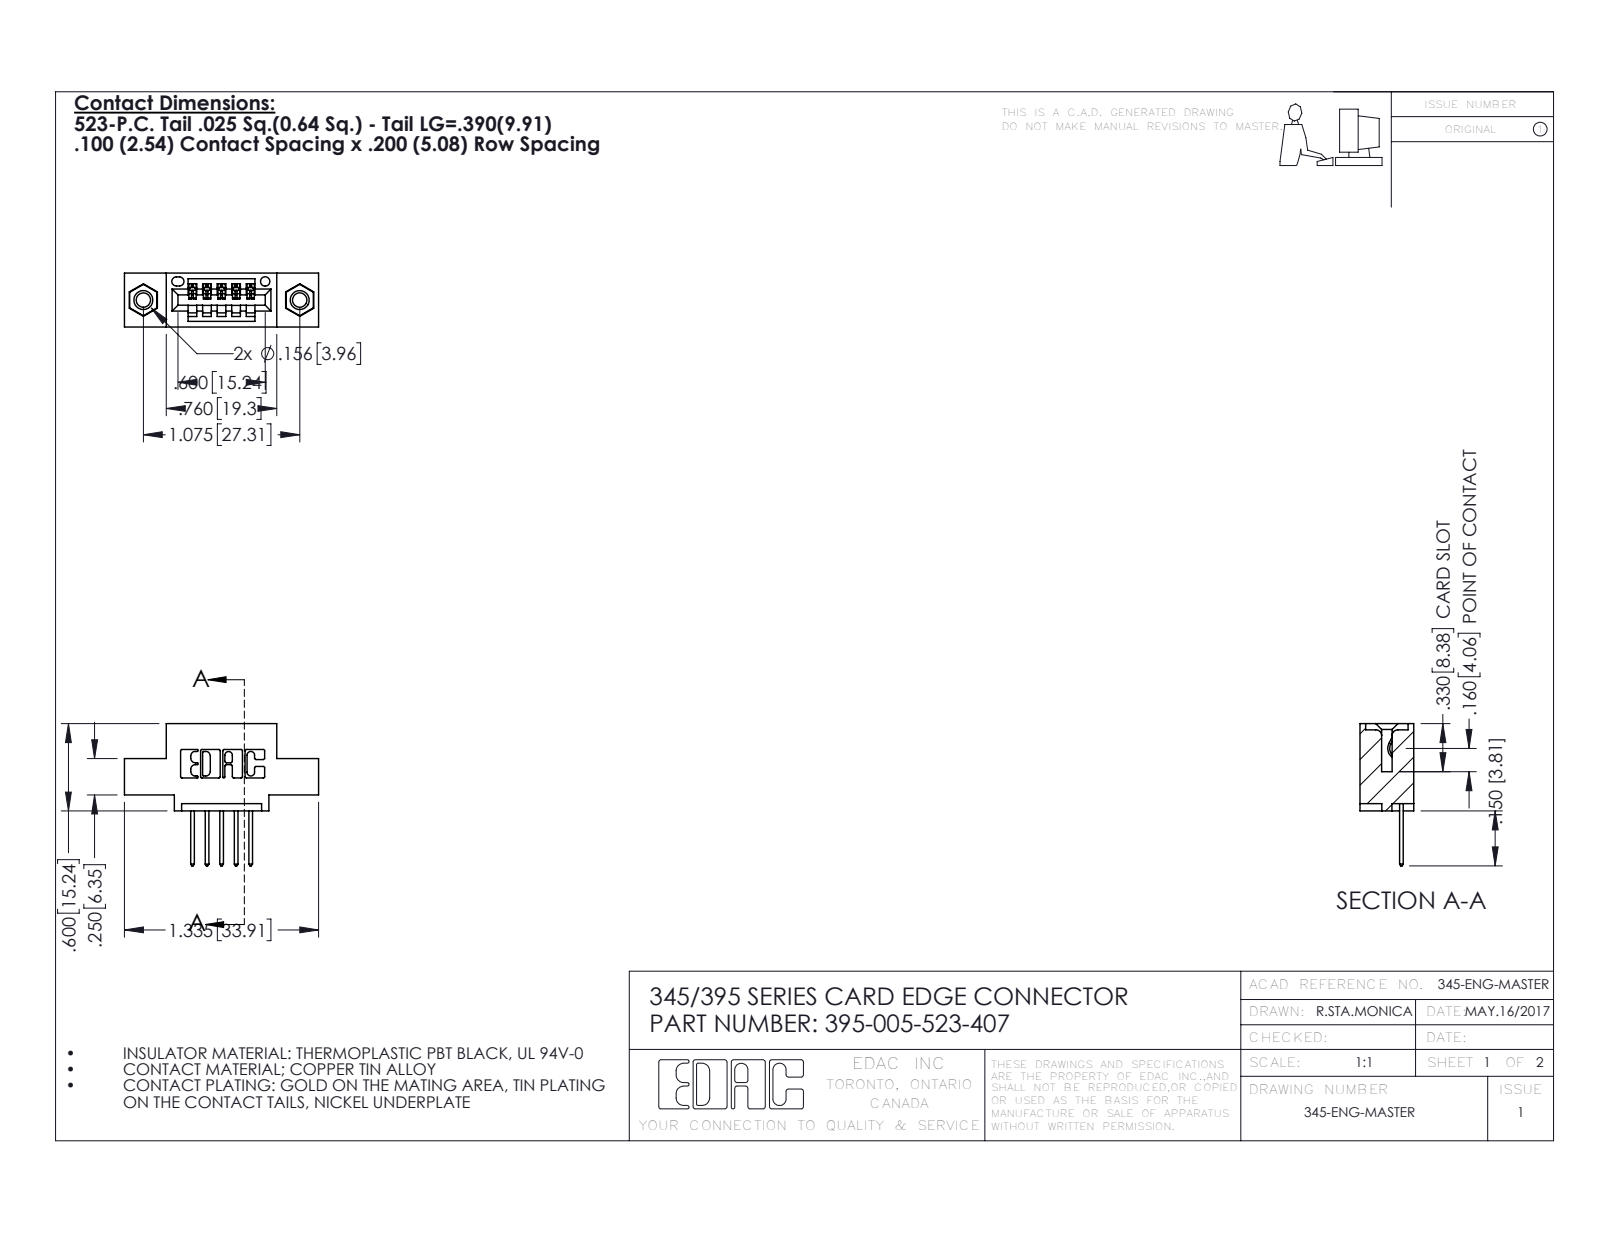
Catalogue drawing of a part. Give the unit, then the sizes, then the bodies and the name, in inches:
Units: inches
Overall size (bounding box): 1.335 × 0.977 × 0.37
Round holes (diameter × count): ⌀0.098 ×2, ⌀0.125 ×2, ⌀0.156 ×2, ⌀0.064 ×1
Round bosses / shafts (diameter × count): ⌀0.155 ×2
Partial cylindrical surfaces — rounded edges, fillets, slot ends (radius × count): R0.01 ×22, R0.006 ×10, R0.01 ×10, R0.007 ×6, R0.031 ×6, R0.026 ×3, R0.031 ×2, R0.04 ×2
Main face-to-face distances: 0.2, 0.37, 0.072, 0.298, 0.1, 0.025, 0.098, 0.272, 0.25, 0.06
Hole centre spacings: 0.27, 0.847, 1.075
Volume: 0.173 in³ · Surface area: 5.233 in²
Bodies: 8 solids, 480 faces (316 planar, 148 cylindrical, 16 other)
Part name (STEP PRODUCT): 395-005-523-407; 345-292-001_345-293-123; 345 Part_0.110 Offset - 0.156 Dia-TI; 345-250-001_345-250-005-103
STEP written by: SolidWorks 2016 (CONFIG_CONTROL_DESIGN)
